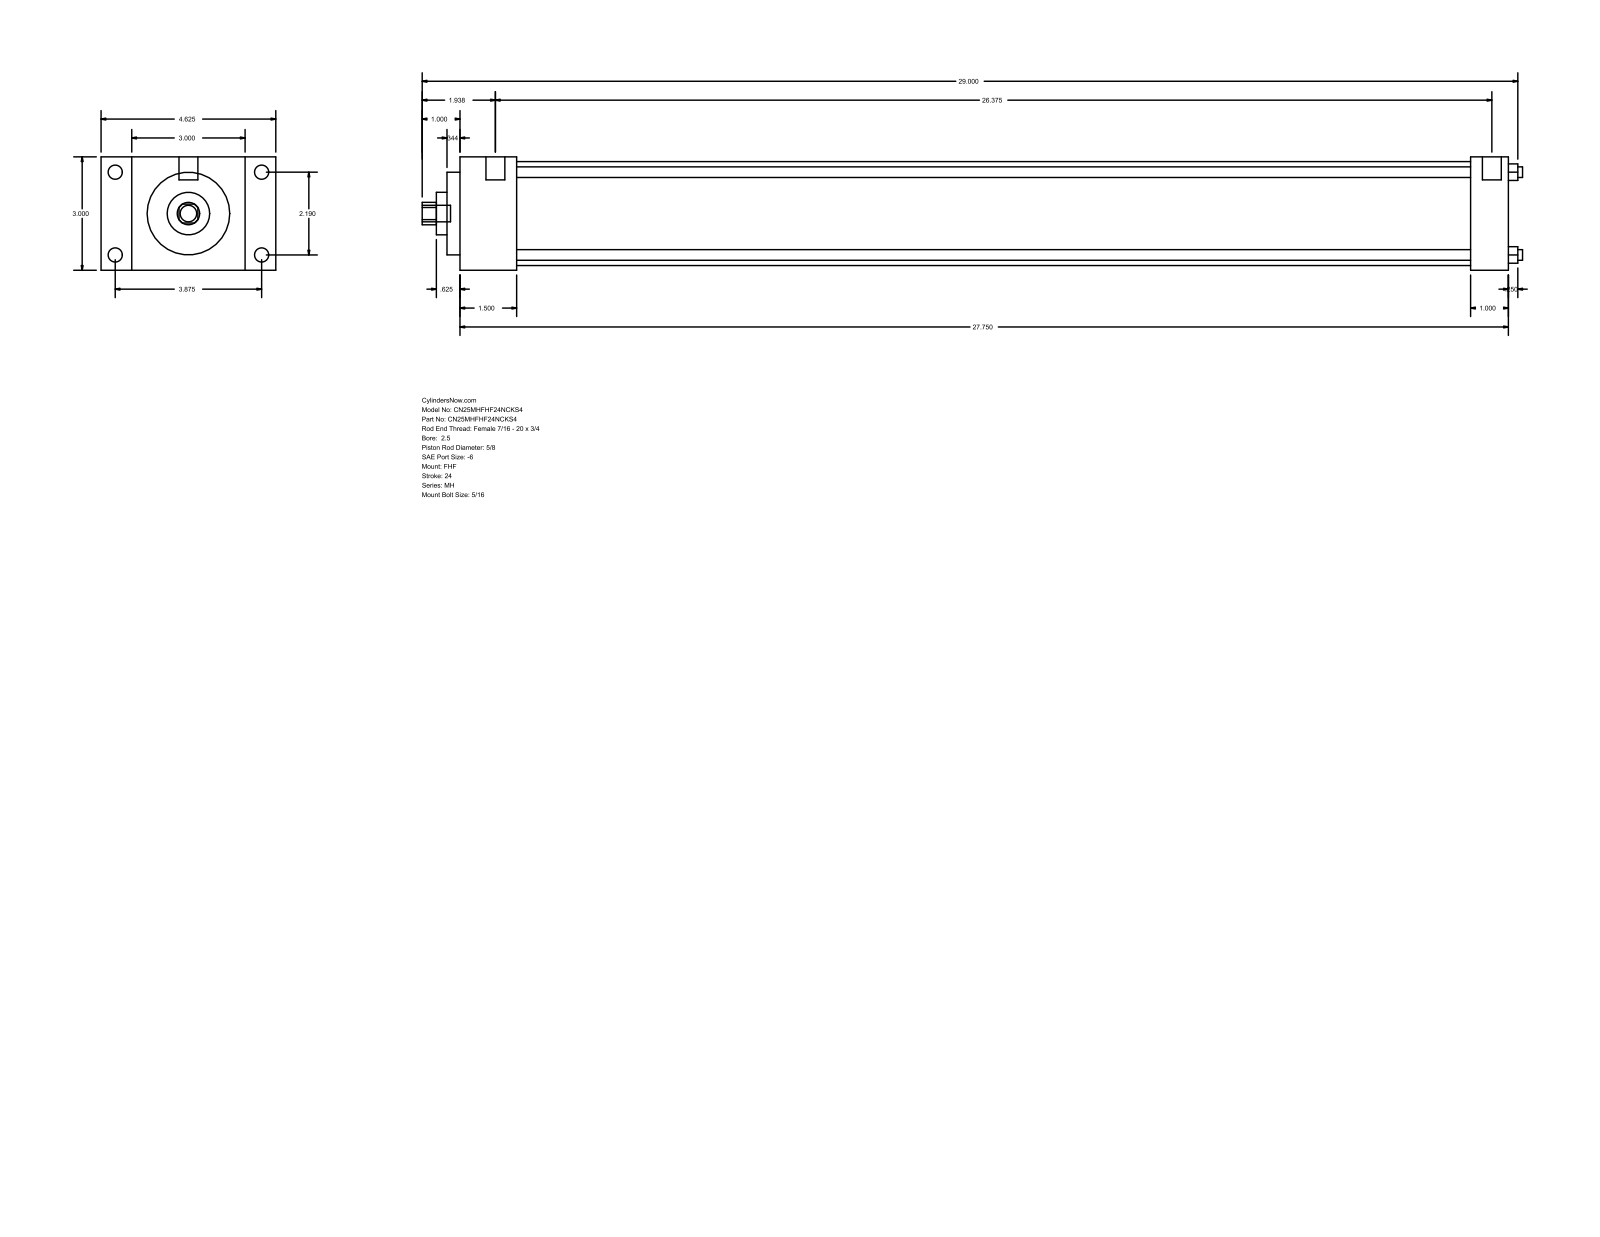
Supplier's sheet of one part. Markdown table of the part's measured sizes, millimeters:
| quantity | value |
| --- | --- |
| part name | MH_FHF__0250_0.625 |
| STEP written by | GSSL Pune (CONFIG_CONTROL_DESIGN) |
| units | millimeters |
| bodies | 0 solids, 90 faces (61 planar, 29 cylindrical, 0 other) |
| overall size | 739.77 × 117.47 × 76.2 |
| round holes (diameter × count) | 7.14 × 4, 15.88 × 1, 28.57 × 1, 55.55 × 1, 69.85 × 1 |
| round bosses / shafts (diameter × count) | 9.53 × 4, 5.56 × 4, 12.7 × 2, 11.11 × 1 |
| partial cylindrical surfaces (radius × count) | 7.54 × 1 |
| main face-to-face distances | 76.2, 704.85, 38.1, 666.75, 20.64, 96.84, 117.48, 25.4, 679.45, 641.35 |
| hole center spacings | 39.33, 55.62, 78.66 |
